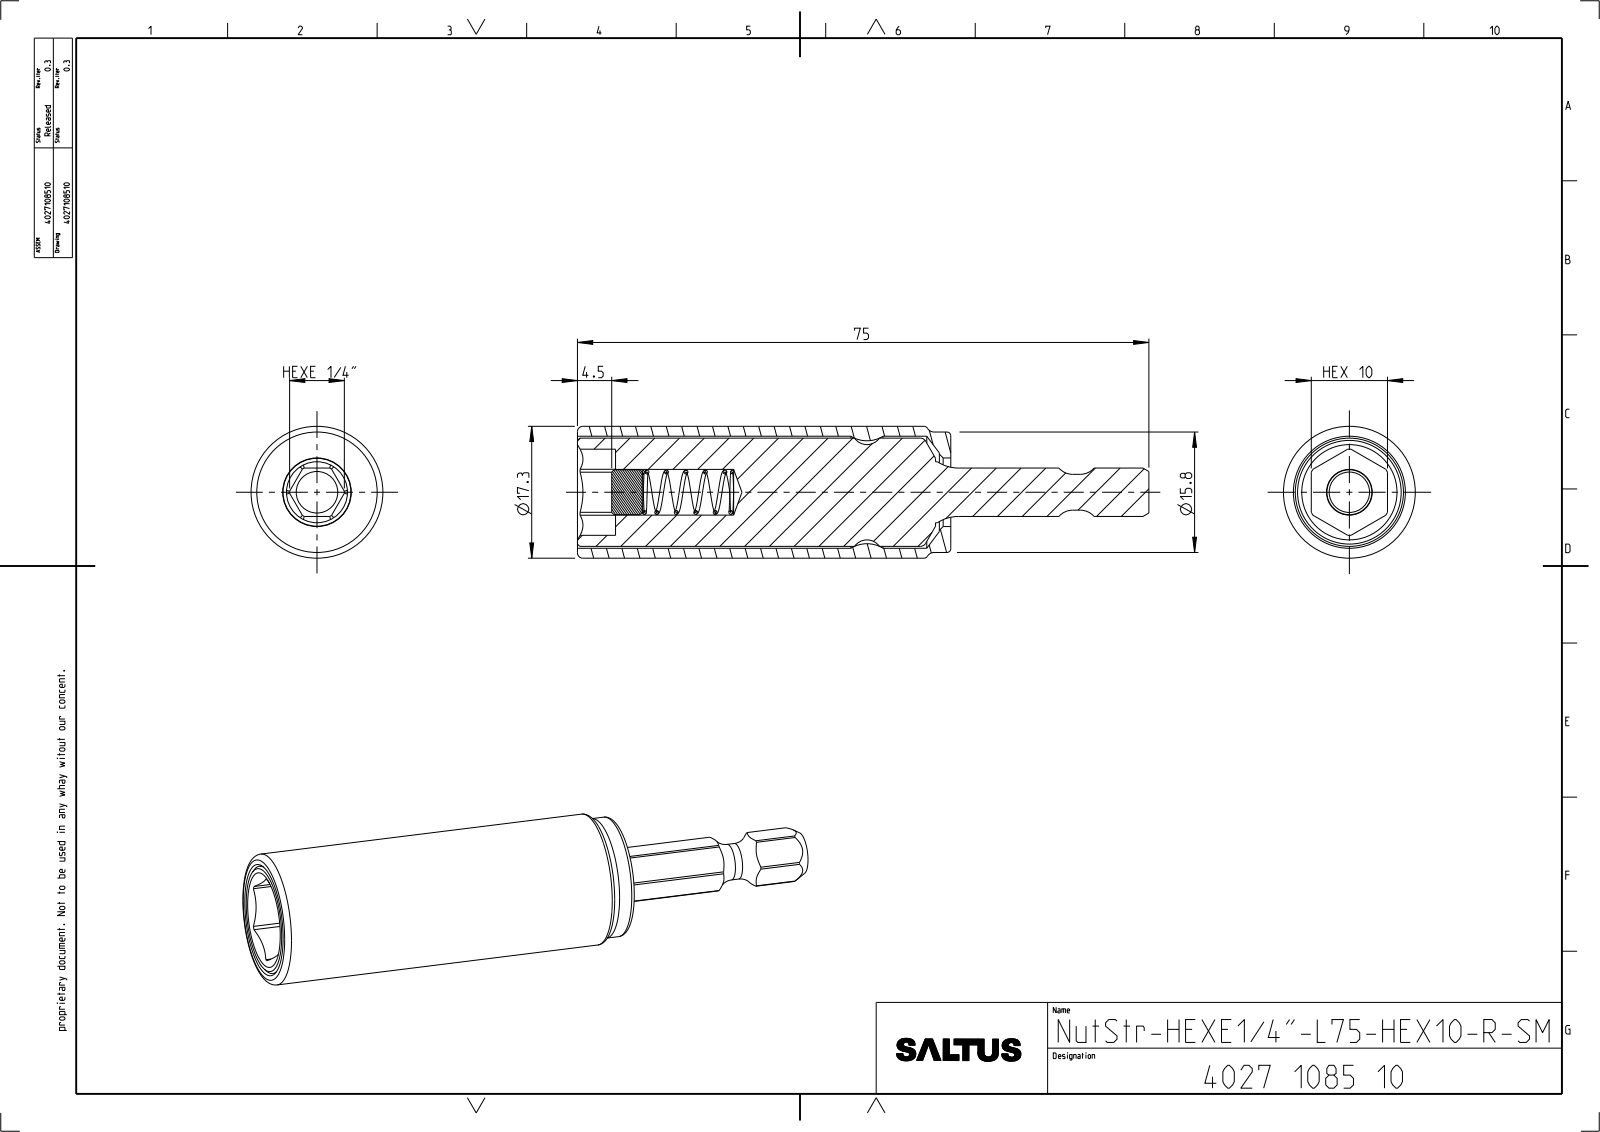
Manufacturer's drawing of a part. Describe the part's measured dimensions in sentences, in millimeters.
The part is named "4027903089_PART; MAGNET_FLEXIBLE_TEMPLATE_AF1; SPRING_FLEXIBLE_TEMPLATE_AF0; 4027903089_ASM (+2 more)". Its 3-D file was written by "CREO PARAMETRIC BY PTC INC, 2022414 (CONFIG_CONTROL_DESIGN)". It is 4 solids with 121 faces: 31 planar, 46 cylindrical and 44 other. Overall it measures 75 by 17.3 by 17.3 millimeters. Its volume is 10 823 cubic millimeters and its surface area 8 784 square millimeters. Round holes: 1 of diameter 6, 1 of diameter 9, 1 of diameter 14.7. Round bosses or shafts: 1 of diameter 17.3, 1 of diameter 15.8, 1 of diameter 14.2, 1 of diameter 8, 1 of diameter 5.9, 1 of diameter 4.7. Partial cylindrical surfaces (rounded edges, fillets, slot ends): 6 of radius 5, 1 of radius 3.59, 1 of radius 5.65. The main face-to-face distances are 6.34, 10, 6.36, 44, 49, 5, 0.5, 40.5, 3.5, 8.5.
